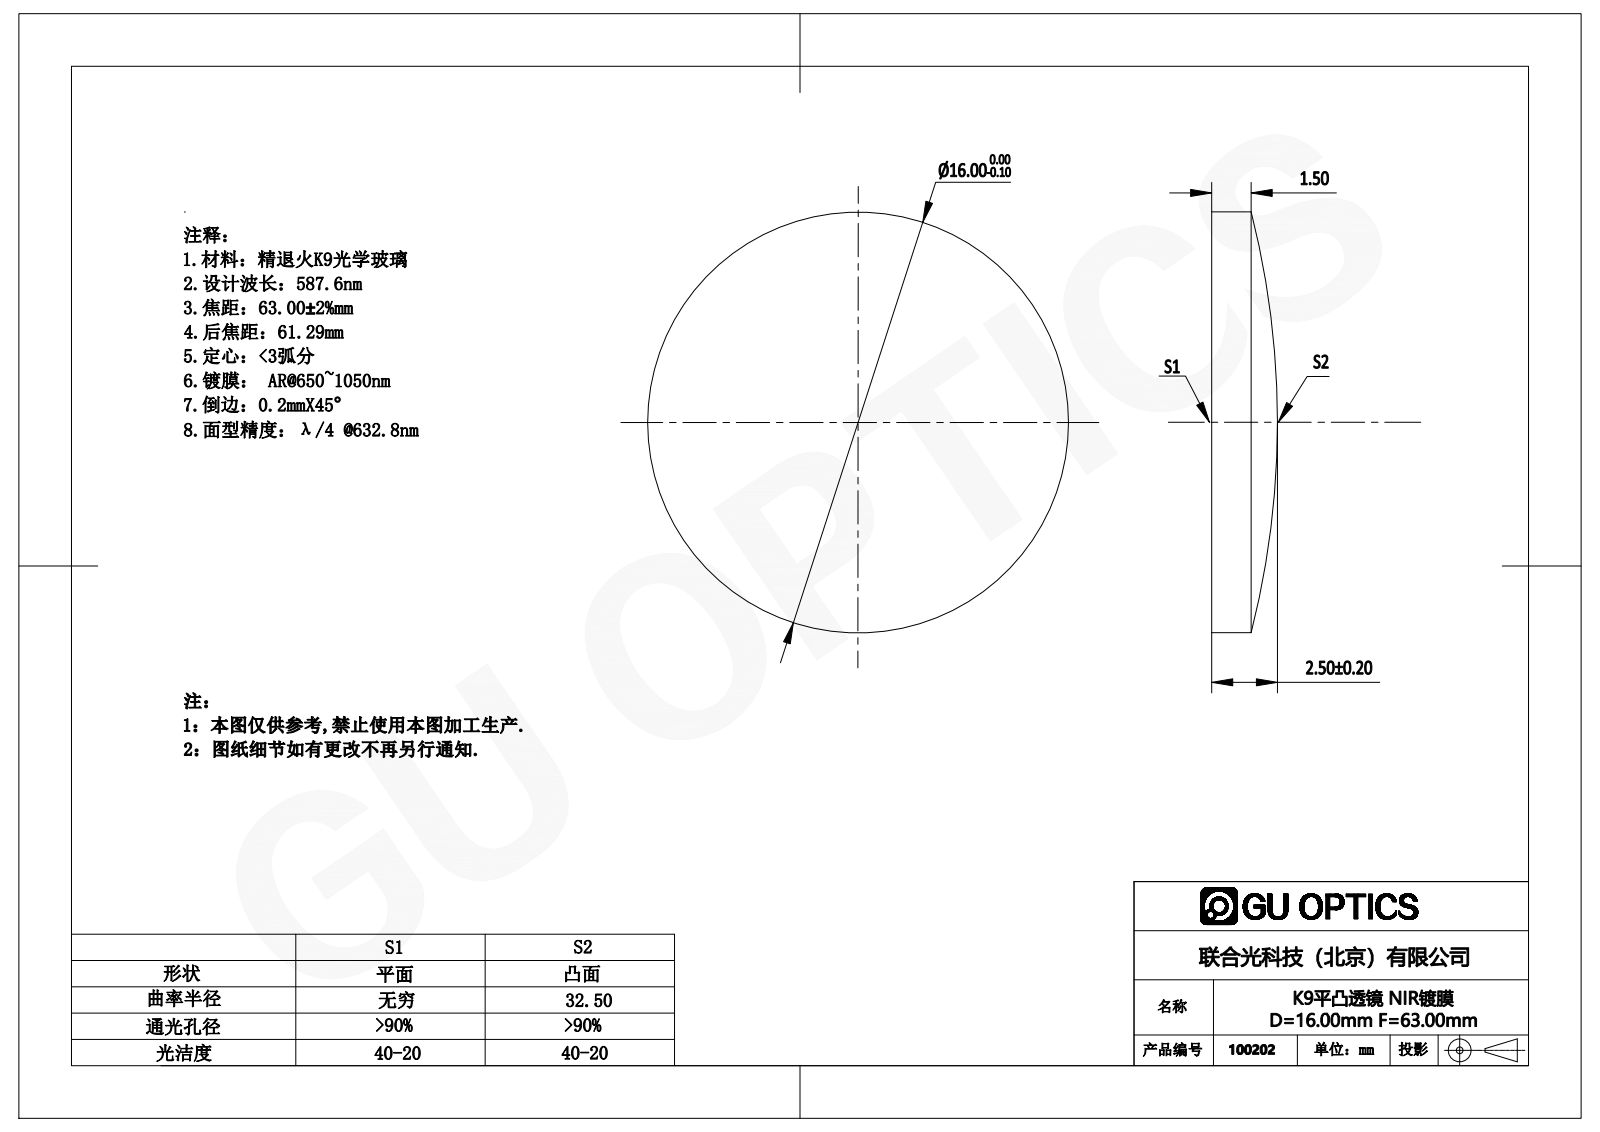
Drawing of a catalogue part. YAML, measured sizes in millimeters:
part_name: "100202"
step_written_by: "SolidWorks 2016 (AUTOMOTIVE_DESIGN)"
units: millimeters
bodies: {solids: 1, faces: 5, planar: 1, cylindrical: 2, other: 2}
overall_size: [16, 16, 2.5]
volume: 403
surface_area: 481
round_bosses_or_shafts:
  - {diameter: 16, count: 1}
